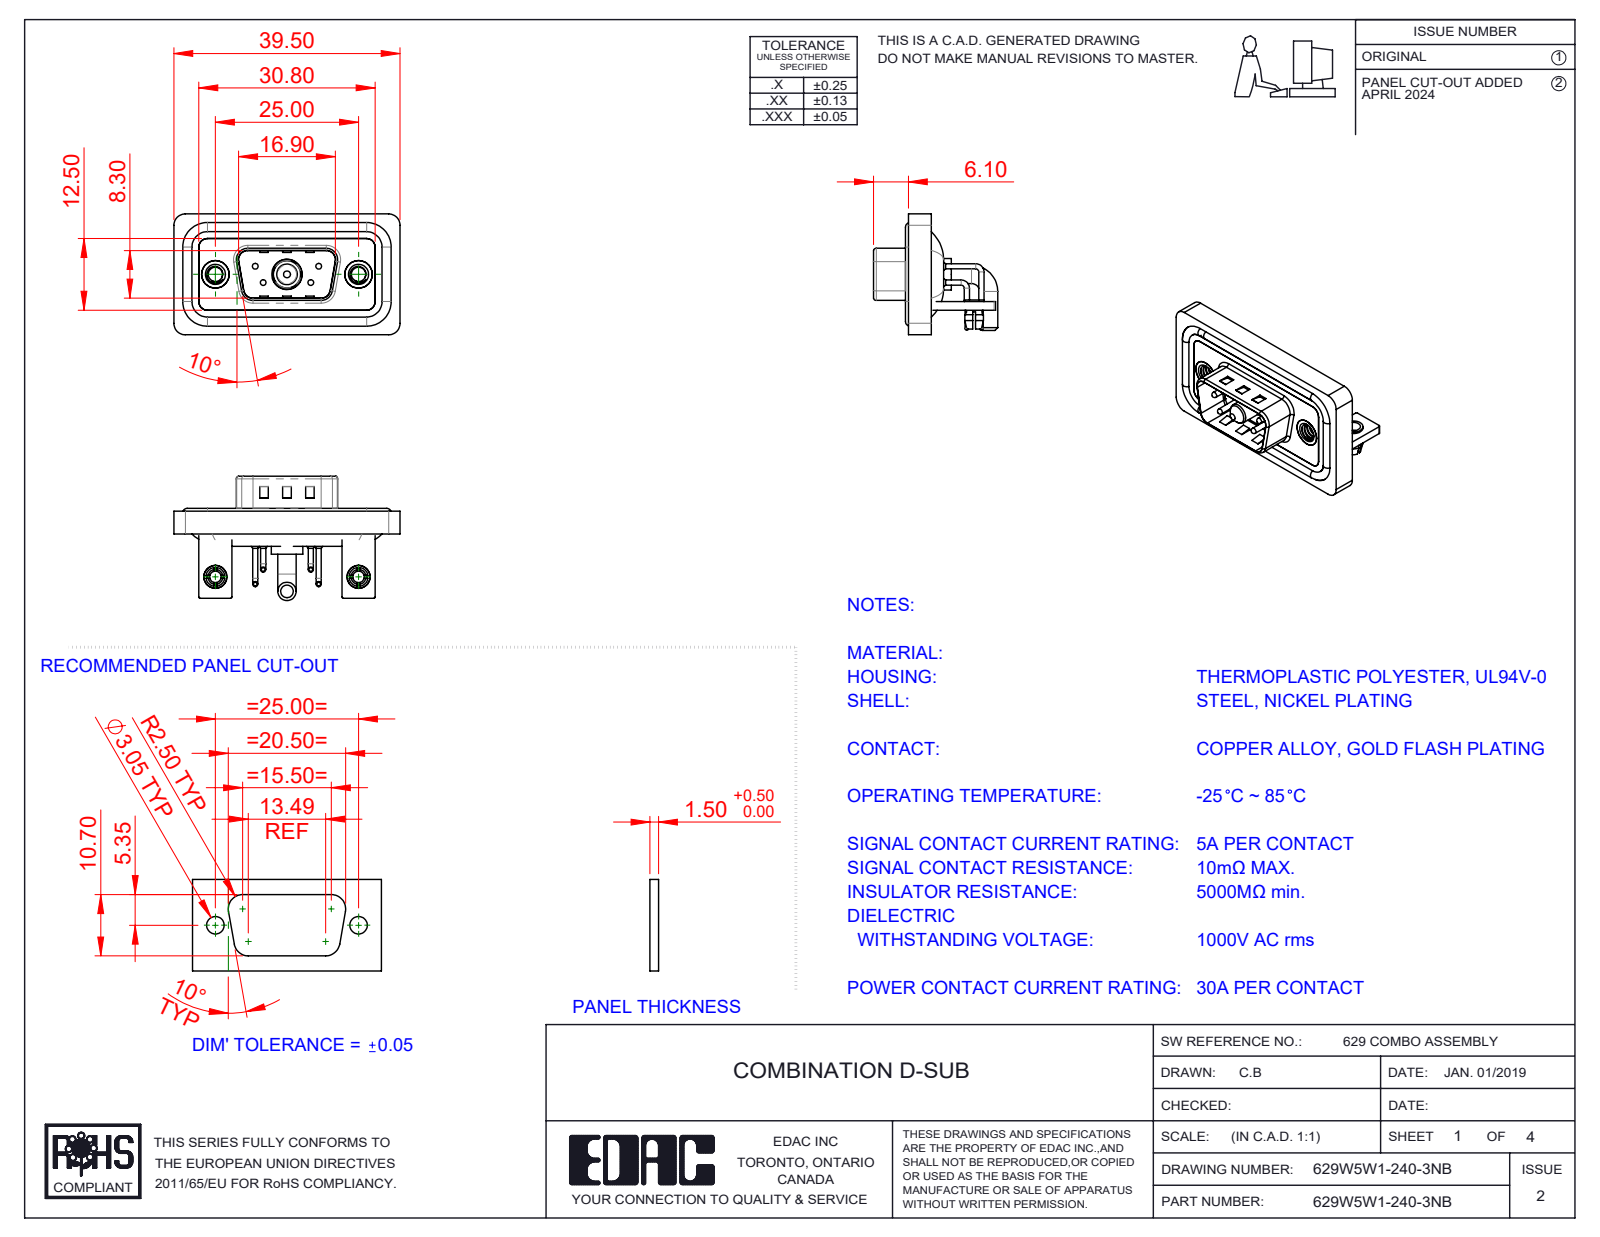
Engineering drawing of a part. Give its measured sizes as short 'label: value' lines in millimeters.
name: 629Combo Contact Row 1; 629Combo Threaded Rivet_B; 629Combo Shell Rear_09 Contacts; 629Combo Stabilizer Bracket (+7 more)
written by: SolidWorks 2023 (CONFIG_CONTROL_DESIGN)
unit: mm
bodies: 17 solids, 1024 faces (479 planar, 395 cylindrical, 150 other)
size: 39.5 × 21.7 × 21.1
volume: 4 812 mm³; area: 7 981 mm²
holes: 6× ⌀2, 4× ⌀0.75, 4× ⌀1.6, 4× ⌀2.5, 2× ⌀3.2, 2× ⌀4, 2× ⌀4.8, 2× ⌀5, 1× ⌀4.85, 1× ⌀5.3
bosses: 8× ⌀0.9, 4× ⌀1.6, 4× ⌀1.5, 4× ⌀1, 4× ⌀0.65, 2× ⌀4.9, 2× ⌀4, 2× ⌀3.4
rounds: 19× R2, 18× R1.5, 16× R0.25, 9× R0.5, 8× R1.6, 4× R0.6, 4× R0.65, 4× R0.9
face distances: 0.4, 1.5, 0.8, 2.9, 1.1, 2.1, 1.2, 1.6, 2.5, 3.7
hole spacings: 3.16, 5.72, 7.1, 12.5, 18.1, 25, 4.39, 4.4
